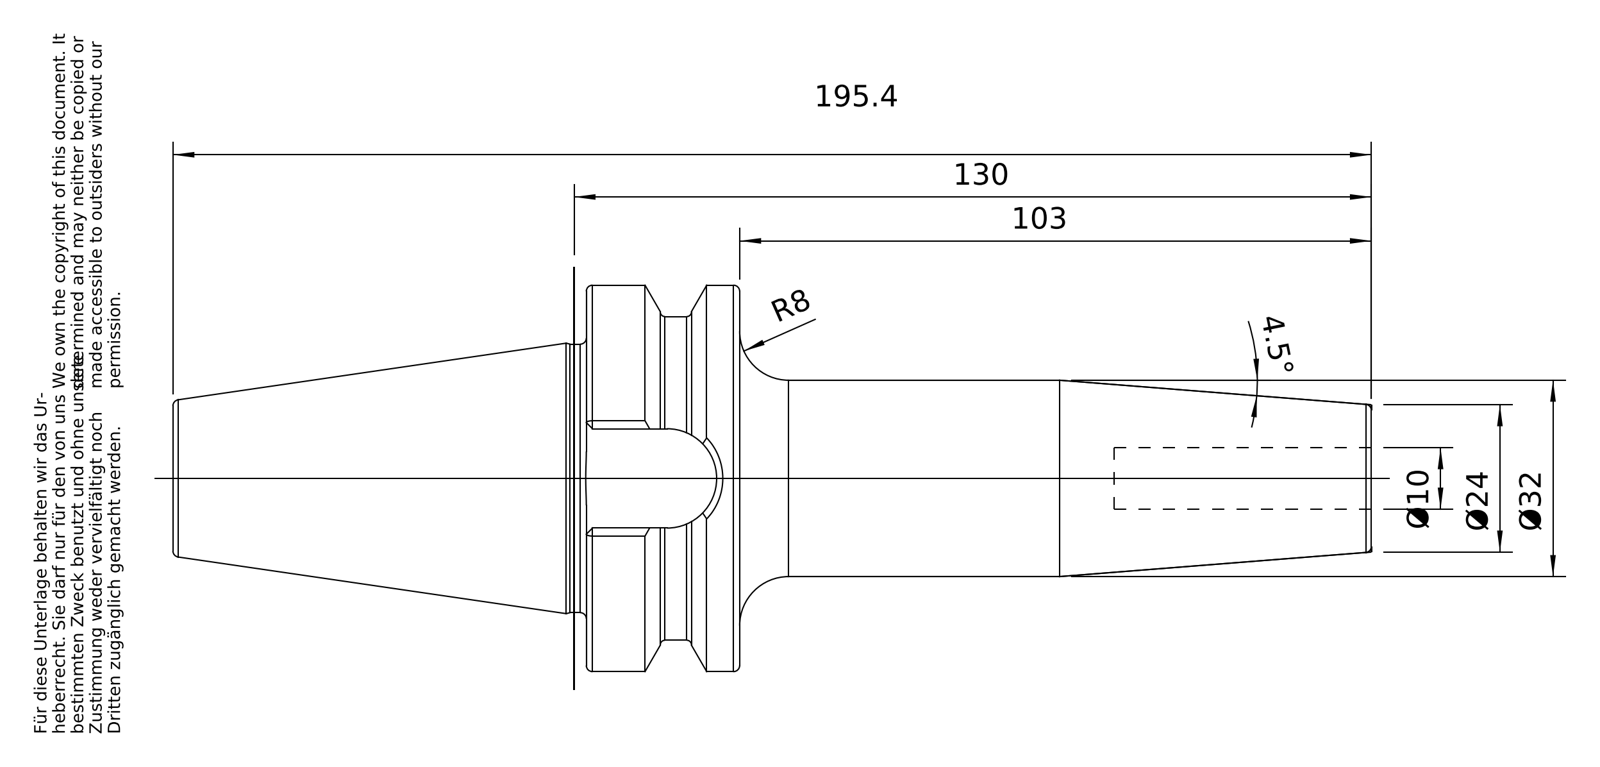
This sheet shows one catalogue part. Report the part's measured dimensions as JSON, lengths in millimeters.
{"part_name": "40-644-10", "step_written_by": "PRO/ENGINEER BY PARAMETRIC TECHNOLOGY CORPORATION, 2010430 (CONFIG_CONTROL_DESIGN)", "units": "millimeters", "bodies": {"solids": 1, "faces": 96, "planar": 26, "cylindrical": 22, "other": 48}, "overall_size": [195.4, 62.98, 62.98], "volume_mm3": 197835, "surface_area_mm2": 32187, "round_holes": [[10, 1], [13.84, 1], [17.01, 1], [17.5, 1]], "round_bosses_or_shafts": [[62.98, 1], [52.75, 1], [43.75, 1], [32, 1], [16.01, 1]], "partial_cylinders_radius": [[8.1, 1]], "face_to_face_distances": [25, 44.9, 128, 103, 16.2, 67.4, 92.4, 195.4, 153.4, 86]}
